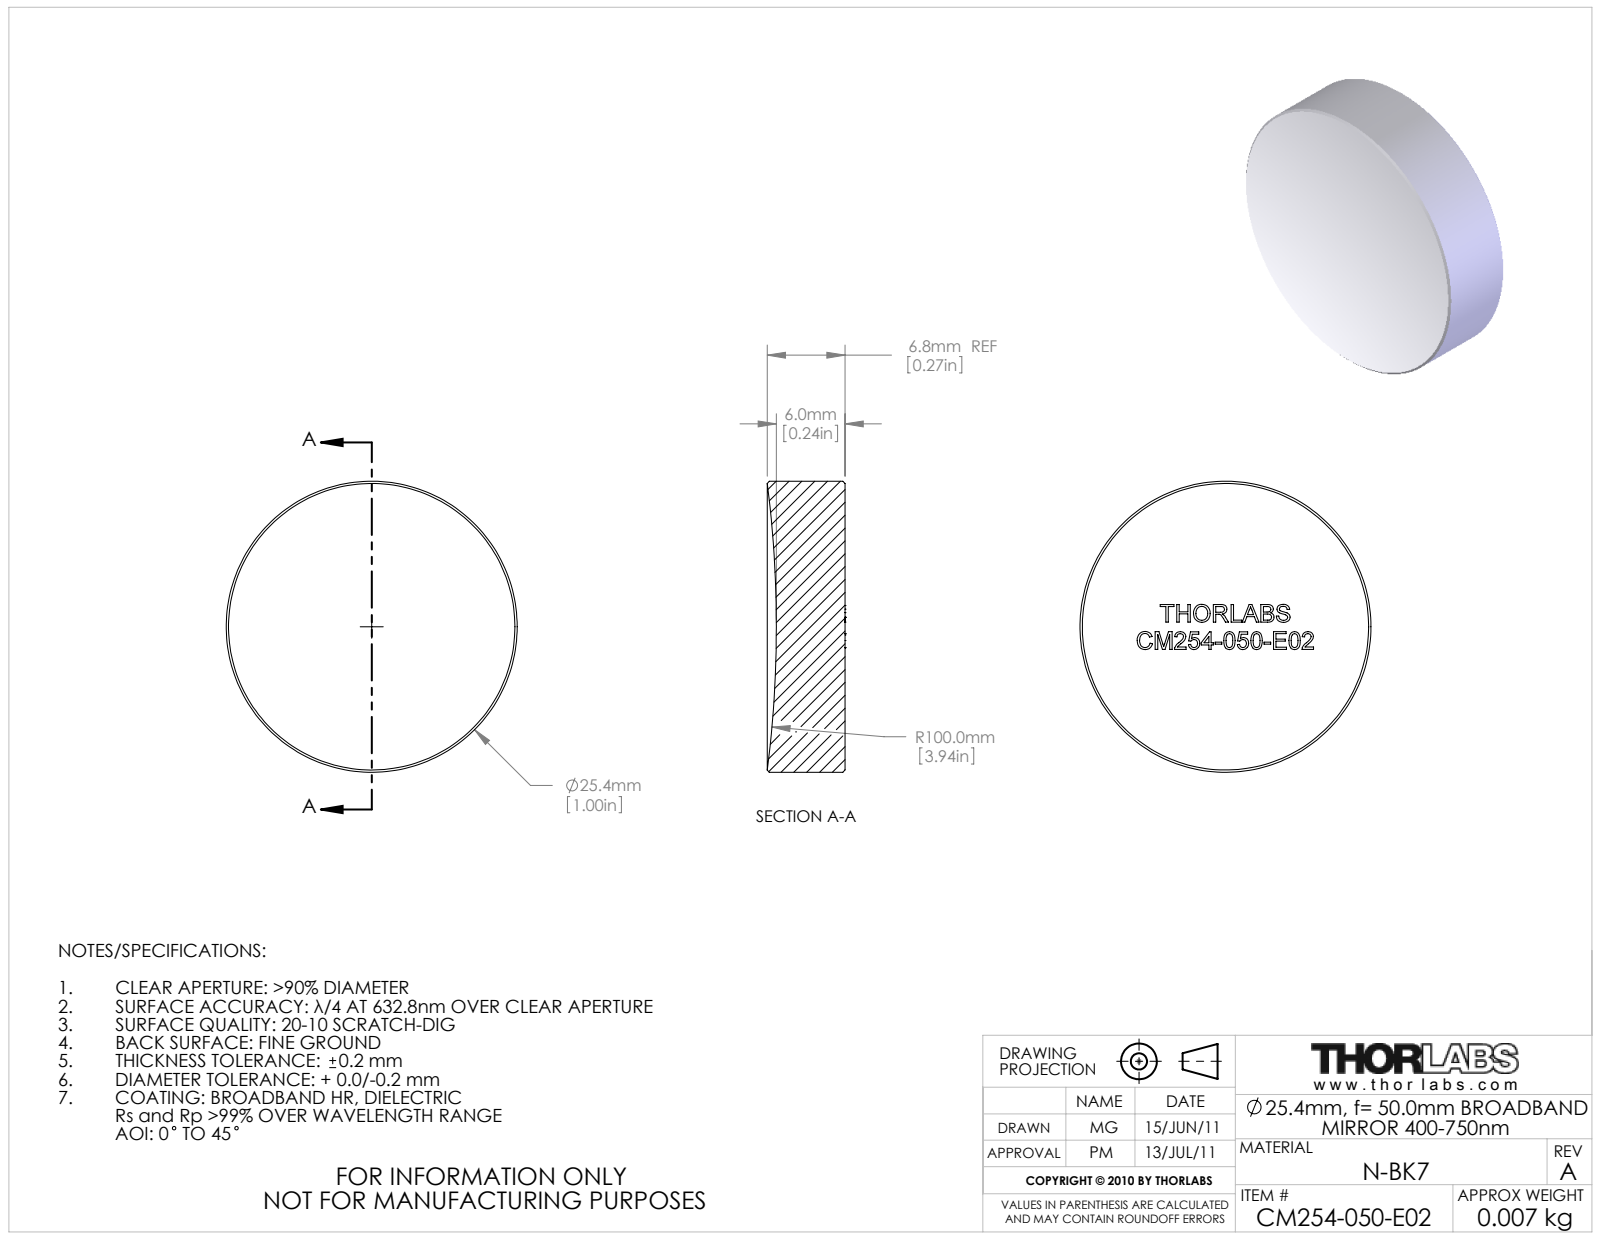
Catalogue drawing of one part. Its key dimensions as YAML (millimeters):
part_name: "22627-E0W"
step_written_by: "SolidWorks 2011 (AUTOMOTIVE_DESIGN)"
units: millimeters
bodies: {solids: 0, faces: 46, planar: 33, cylindrical: 2, other: 11}
overall_size: [25.4, 25.4, 6.79]
round_bosses_or_shafts:
  - {diameter: 25.4, count: 1}
